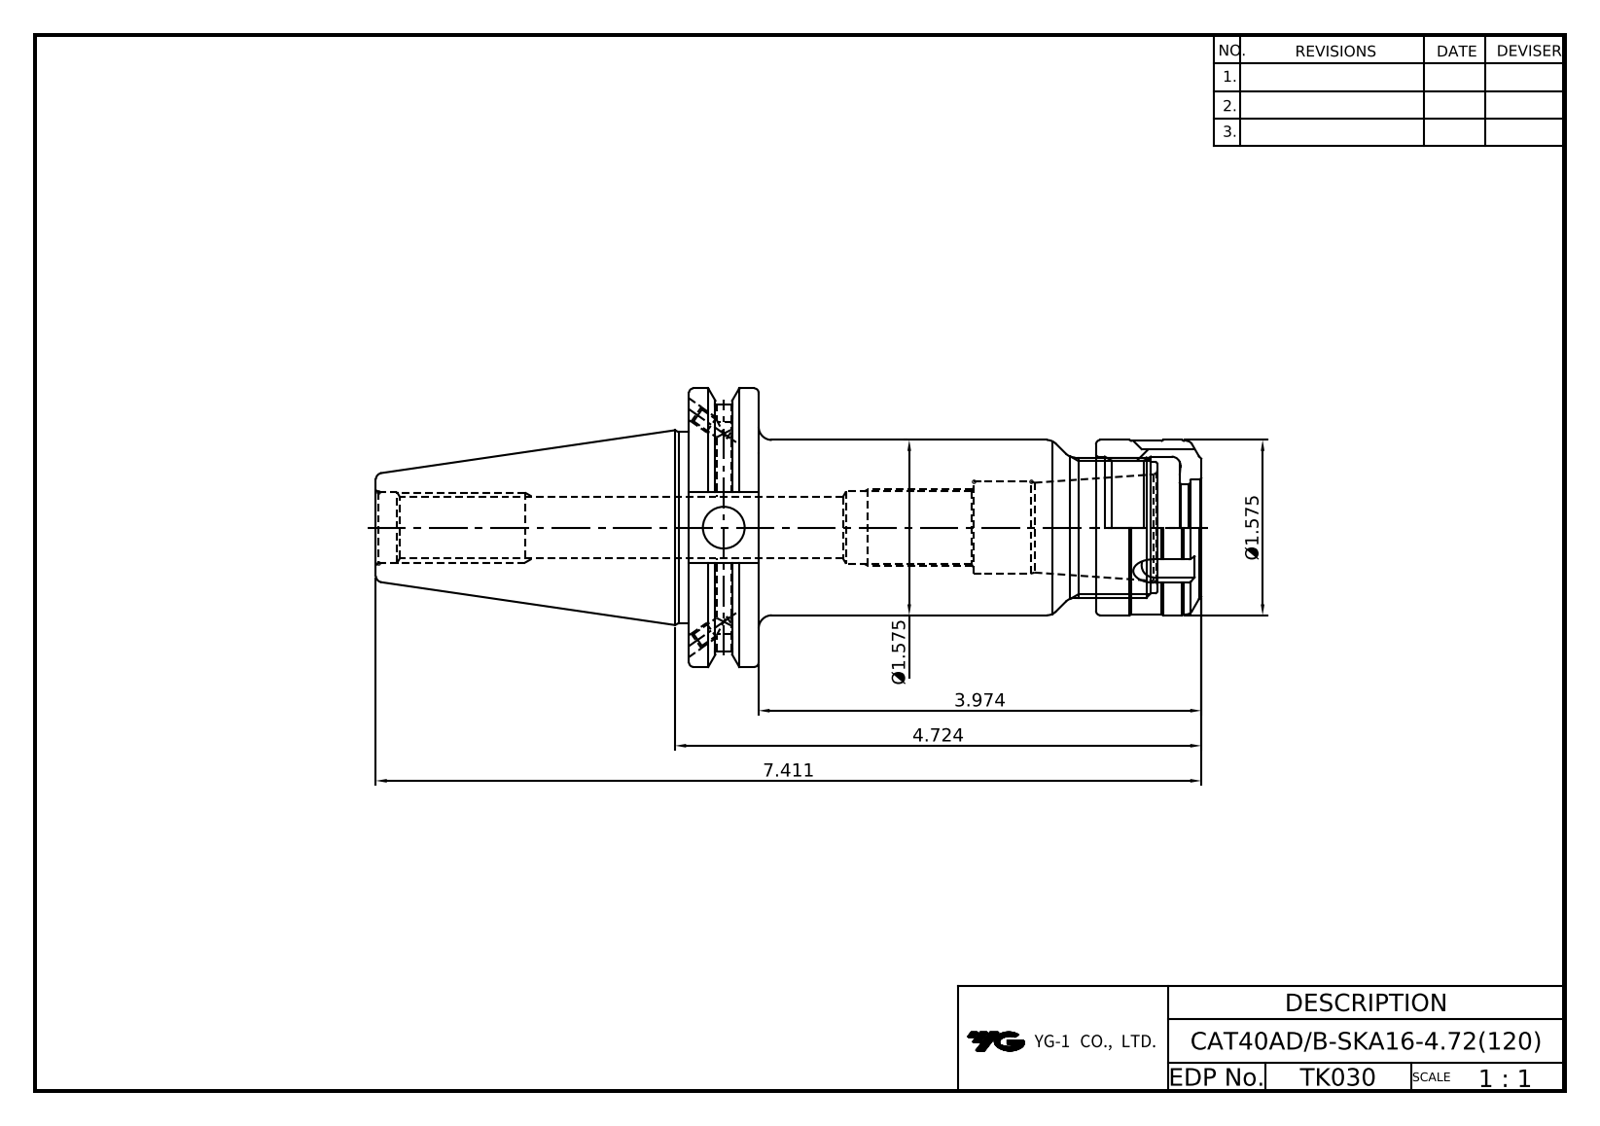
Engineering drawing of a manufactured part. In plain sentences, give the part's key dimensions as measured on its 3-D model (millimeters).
The part is named "LO-CAT40ADB-SKA16-120; SKN16-NUT". Its 3-D file was written by "Autodesk Inventor 2025 (AP242_MANAGED_MODEL_BASED_3D_ENGINEERING_MIM_LF)". It is 2 solids with 155 faces: 58 planar, 47 cylindrical and 50 other. Overall it measures 188.25 by 63.5 by 61.09 millimeters. Its volume is 191 888 cubic millimeters and its surface area 43 380 square millimeters. Round holes: 4 of diameter 3.24, 2 of diameter 4, 2 of diameter 4.2, 1 of diameter 9.53, 1 of diameter 13.39, 1 of diameter 15.75, 1 of diameter 16.3, 1 of diameter 19.8, 1 of diameter 21, 1 of diameter 22, 1 of diameter 32, 1 of diameter 32.4. Round bosses or shafts: 1 of diameter 63.5, 1 of diameter 43.6, 1 of diameter 40, 1 of diameter 39.6. Partial cylindrical surfaces (rounded edges, fillets, slot ends): 1 of radius 28.15. The main face-to-face distances are 15.88, 111.93, 96.05, 116.83, 100.95, 4.9, 106.83, 90.95, 5.1, 10.
